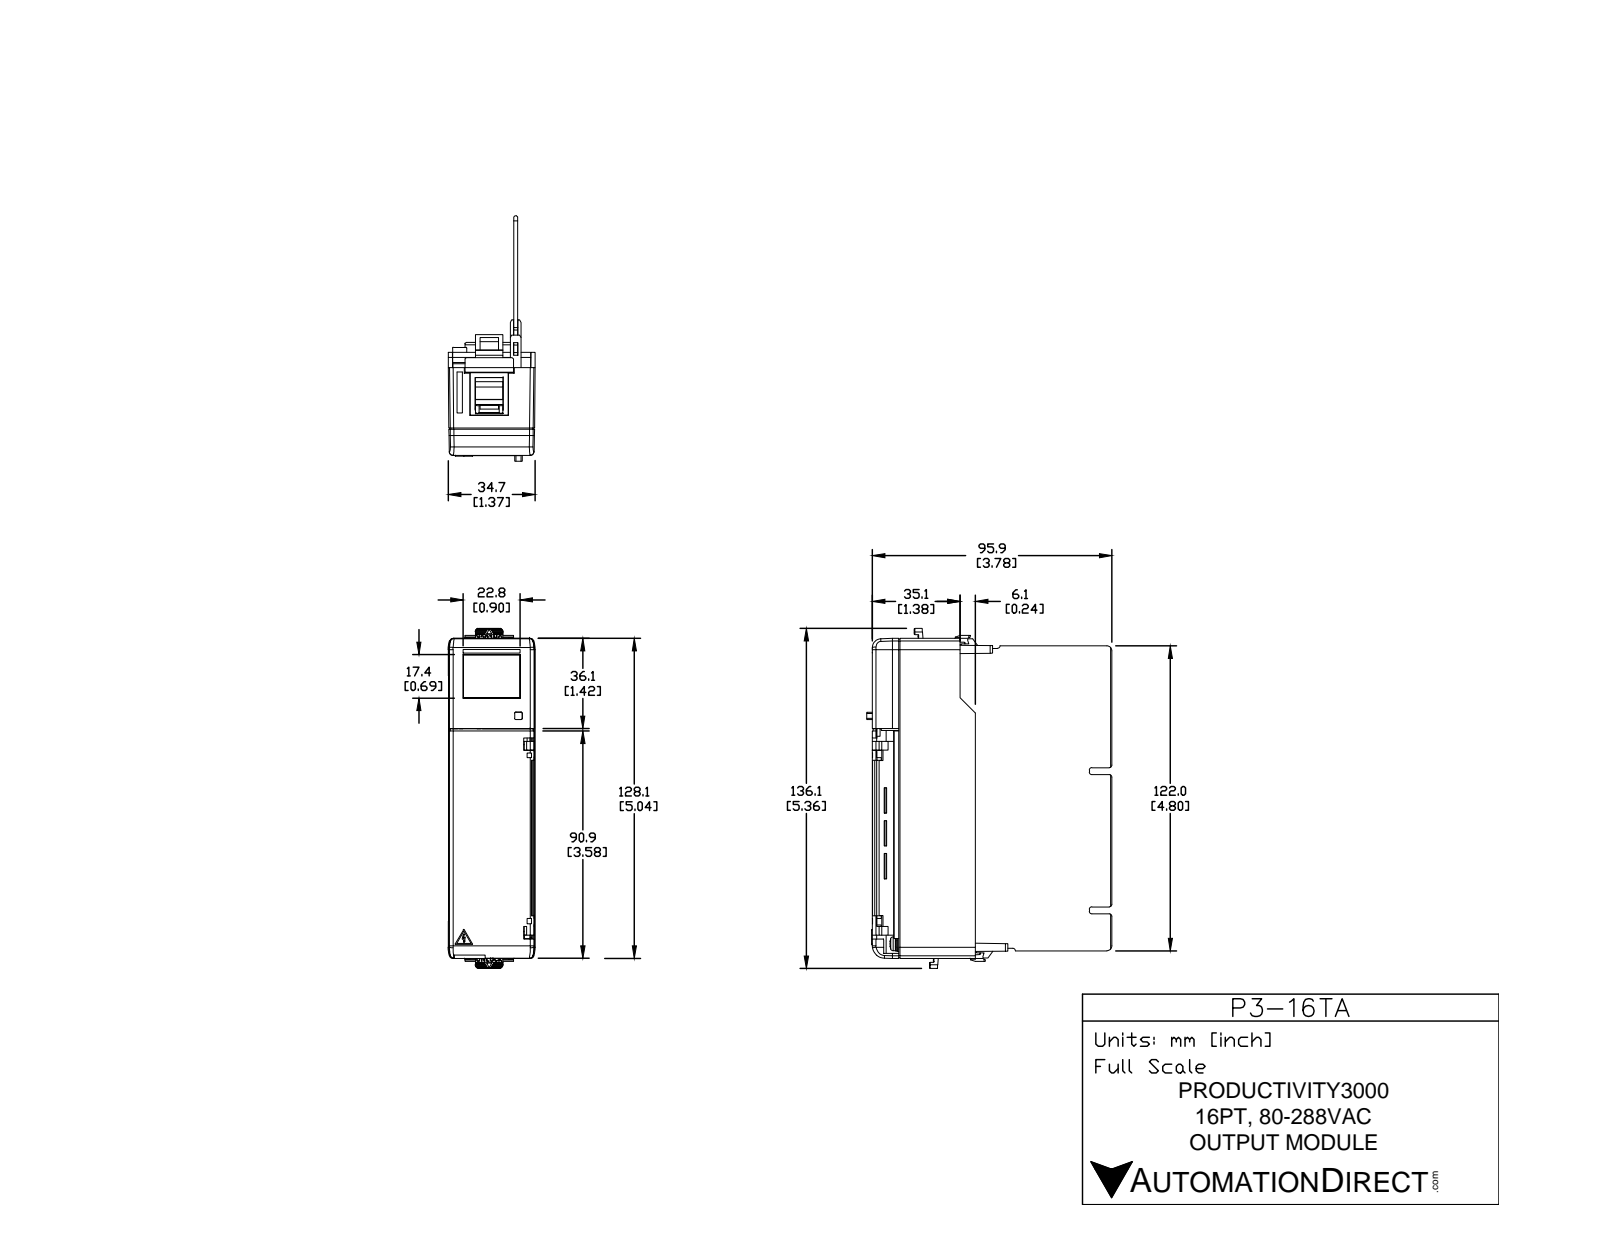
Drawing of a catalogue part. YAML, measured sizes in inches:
part_name: "P3-16TA"
step_written_by: "SolidWorks 2009 (CONFIG_CONTROL_DESIGN)"
units: inches
bodies: {solids: 1, faces: 3804, planar: 2821, cylindrical: 737, other: 246}
overall_size: [5.357, 3.787, 1.37]
volume: 6.184
surface_area: 116.9
round_holes:
  - {diameter: 0.126, count: 22}
  - {diameter: 0.197, count: 2}
  - {diameter: 0.071, count: 1}
round_bosses_or_shafts:
  - {diameter: 0.217, count: 22}
  - {diameter: 0.118, count: 22}
  - {diameter: 0.094, count: 20}
  - {diameter: 0.22, count: 2}
  - {diameter: 0.087, count: 2}
  - {diameter: 0.079, count: 2}
  - {diameter: 0.059, count: 1}
partial_cylinders:
  - {radius: 0.02, count: 91}
  - {radius: 0.039, count: 33}
  - {radius: 0.012, count: 29}
  - {radius: 0.066, count: 22}
  - {radius: 0.059, count: 13}
  - {radius: 0.079, count: 6}
  - {radius: 0.008, count: 5}
  - {radius: 0.004, count: 4}
face_to_face_distances: [0.063, 0.067, 1.111, 1.044, 1.282, 0.874, 0.087, 0.311, 0.268, 0.209]
hole_center_spacings: [0.342, 0.3, 0.545, 0.6, 0.811, 0.9, 1.094, 1.2]
